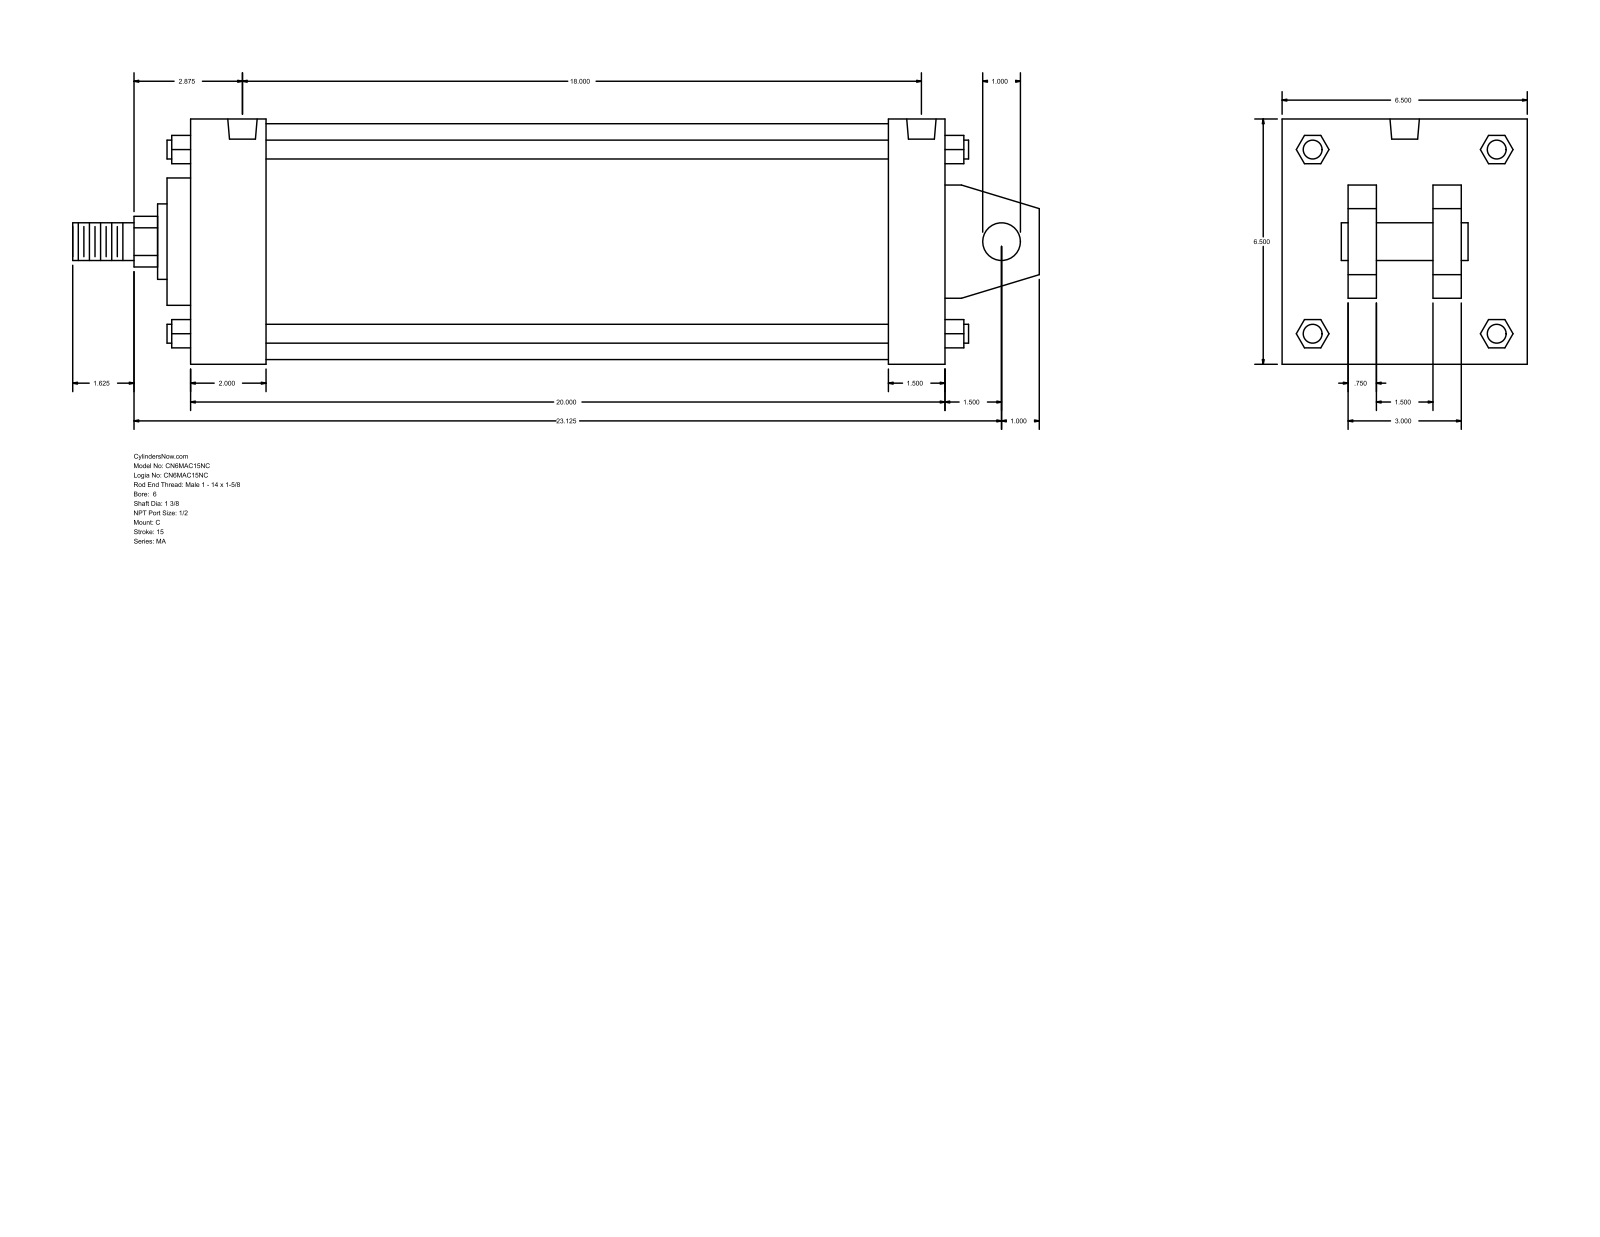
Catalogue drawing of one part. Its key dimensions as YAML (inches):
part_name: "MA_C__0600_1.375"
step_written_by: "GSSL Pune (CONFIG_CONTROL_DESIGN)"
units: inches
bodies: {solids: 0, faces: 141, planar: 109, cylindrical: 32, other: 0}
overall_size: [25.625, 6.5, 6.5]
round_holes:
  - {diameter: 0.687, count: 4}
  - {diameter: 0.778, count: 2}
round_bosses_or_shafts:
  - {diameter: 0.5, count: 4}
  - {diameter: 1, count: 2}
  - {diameter: 6.25, count: 1}
  - {diameter: 3.375, count: 1}
  - {diameter: 2, count: 1}
  - {diameter: 1.375, count: 1}
partial_cylinders:
  - {radius: 0.672, count: 1}
face_to_face_distances: [6.5, 20, 1.5, 0.75, 2.5, 4, 2, 1.75, 4.75, 18.5]
hole_center_spacings: [18, 0.125, 17.875, 18.125]
